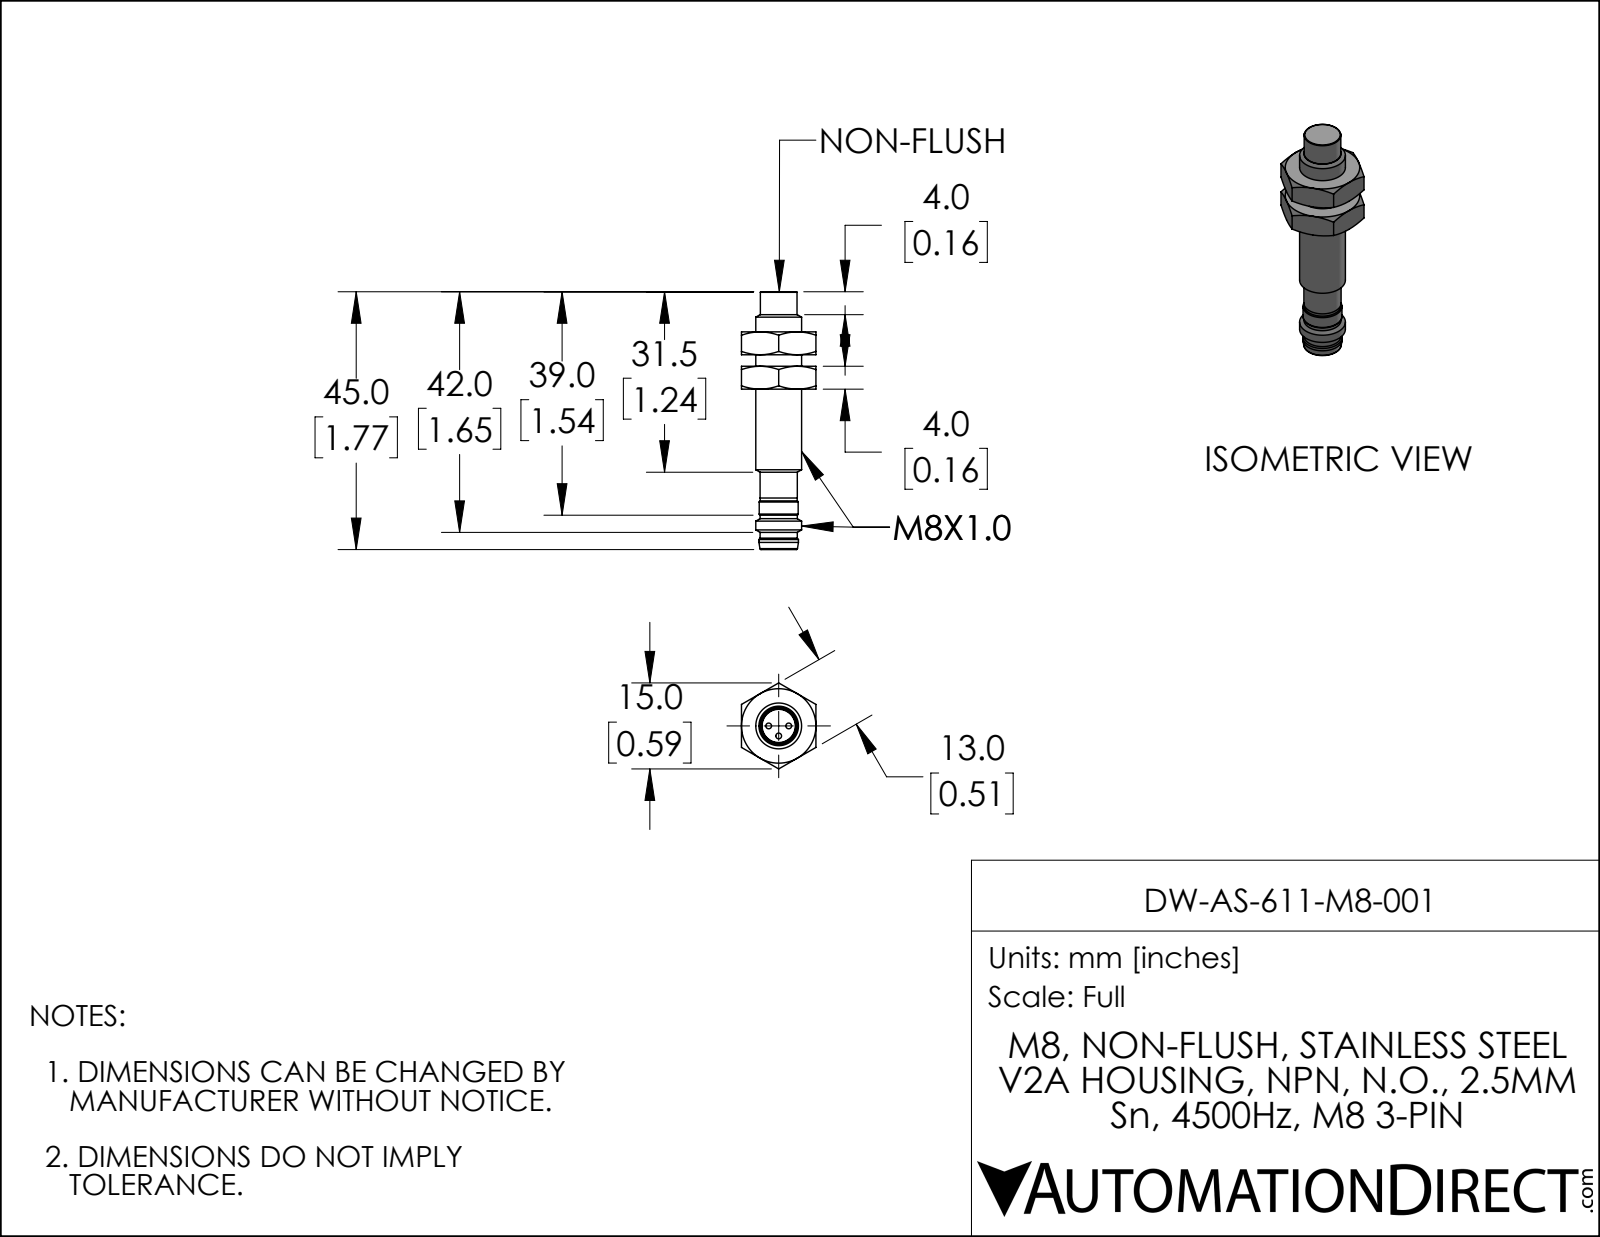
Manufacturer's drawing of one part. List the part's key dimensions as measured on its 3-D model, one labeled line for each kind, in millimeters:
Part name (STEP PRODUCT): DW-AS-611-M8-001
STEP written by: SolidWorks 2019 (AUTOMOTIVE_DESIGN)
Units: millimetres
Bodies: 1 solid, 76 faces (24 planar, 15 cylindrical, 37 other)
Overall size (bounding box): 45 × 15 × 13
Volume: 2 640 mm³ · Surface area: 1 817 mm²
Round holes (diameter × count): ⌀5.8 ×1
Round bosses / shafts (diameter × count): ⌀1 ×3, ⌀8 ×1, ⌀6.9 ×1, ⌀6.8 ×1, ⌀6.5 ×1, ⌀6.5 ×1, ⌀6.4 ×1
Main face-to-face distances: 13, 4, 6, 2, 10, 7, 11, 17, 29, 23
